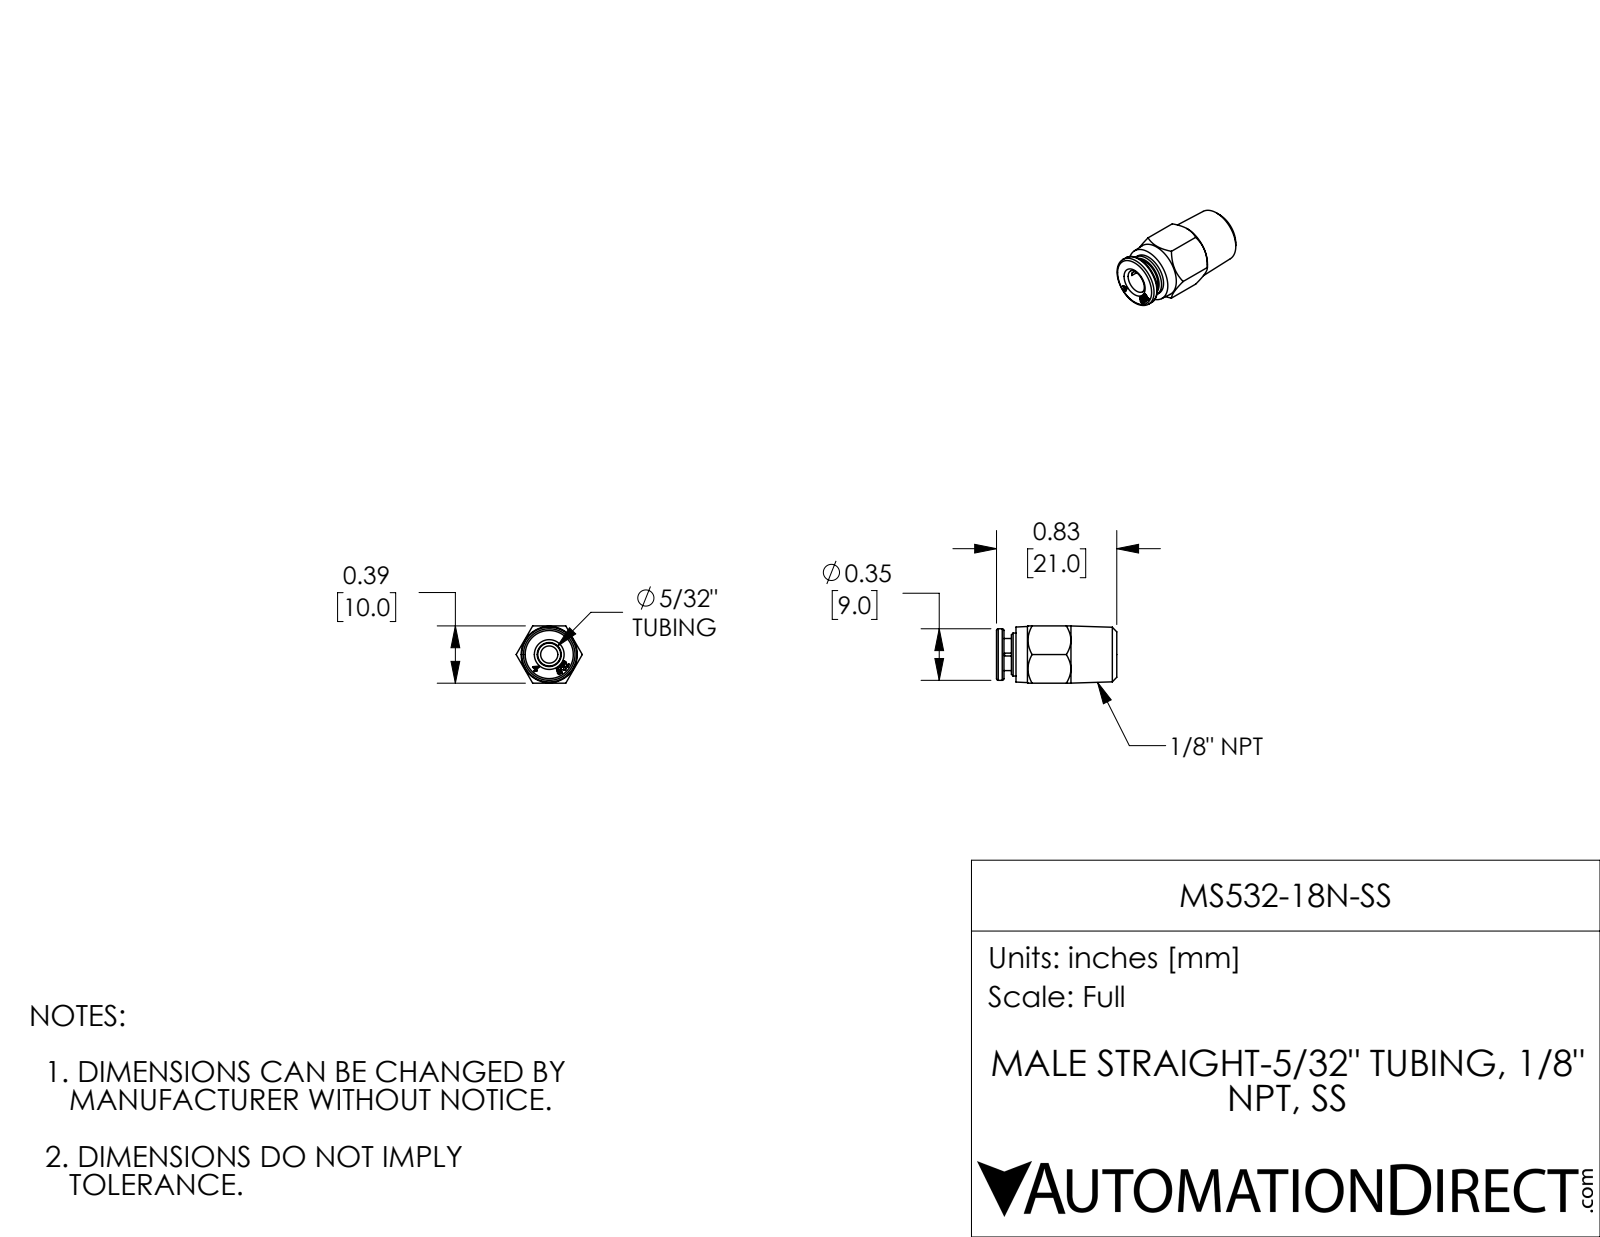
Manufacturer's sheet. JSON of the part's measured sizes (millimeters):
{"part_name": "MS532-18N-SS", "step_written_by": "SolidWorks 2017 (AUTOMOTIVE_DESIGN)", "units": "millimeters", "bodies": {"solids": 1, "faces": 131, "planar": 57, "cylindrical": 10, "other": 64}, "overall_size": [21, 11.6, 10], "volume_mm3": 1300, "surface_area_mm2": 1117, "round_holes": [[3, 1], [4.2, 1]], "round_bosses_or_shafts": [[9, 1], [7.5, 1], [5.6, 1]], "face_to_face_distances": [10, 1.3, 21, 19.7, 17.6, 2.1, 3.4, 0.8, 18.4, 2.6]}
